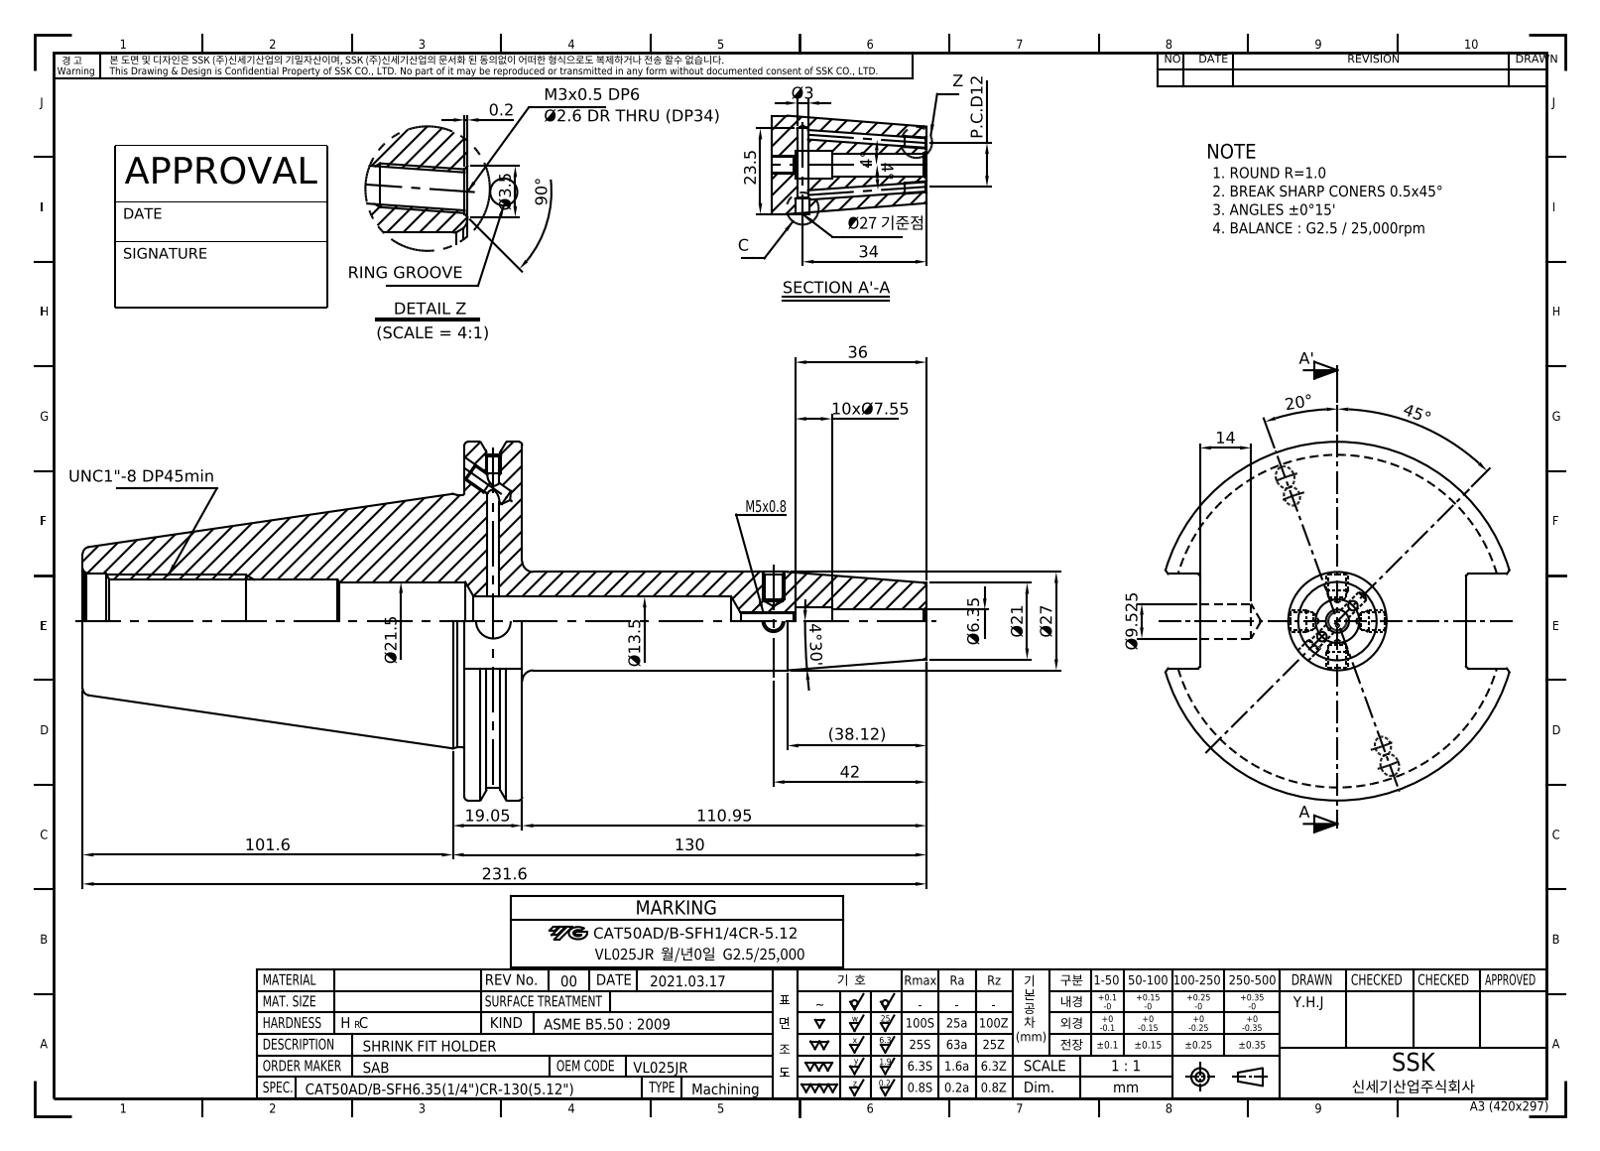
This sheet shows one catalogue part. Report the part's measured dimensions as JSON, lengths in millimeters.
{"part_name": "LO-CAT50ADB-SFH6.35CR-130", "step_written_by": "Autodesk Inventor 2022 (AUTOMOTIVE_DESIGN)", "units": "millimeters", "bodies": {"solids": 1, "faces": 95, "planar": 37, "cylindrical": 33, "other": 25}, "overall_size": [231.6, 98.42, 94.69], "volume_mm3": 370669, "surface_area_mm2": 57715, "round_holes": [[2.46, 2], [3.24, 2], [4.13, 2], [4.2, 2], [5, 2], [3, 1], [4, 1], [4.3, 1], [6.35, 1], [7.5, 1], [9.53, 1], [13.5, 1]], "round_bosses_or_shafts": [[98.42, 1], [91.29, 1], [69.25, 1], [27, 1]], "face_to_face_distances": [15.88, 104.77, 120.65, 73.03, 25.9, 231.6, 126.83, 110.95, 110.82, 6.05]}
